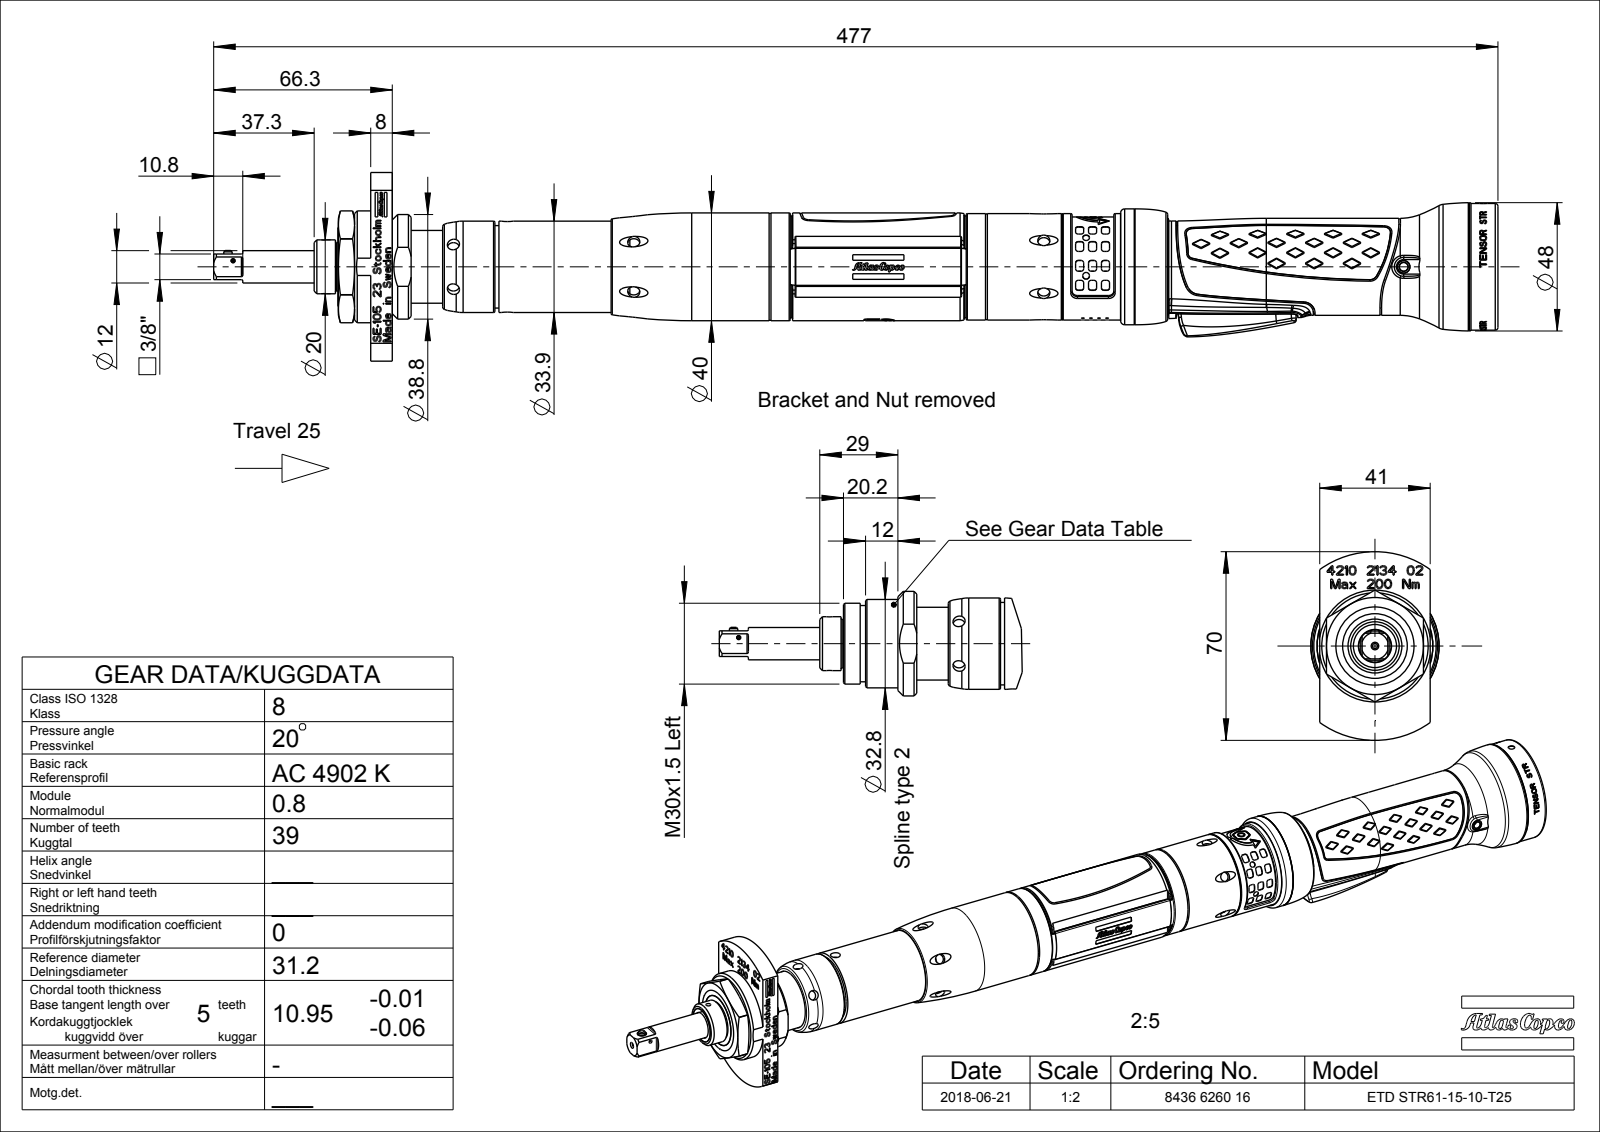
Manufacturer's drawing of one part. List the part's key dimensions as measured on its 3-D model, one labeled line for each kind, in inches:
Part name (STEP PRODUCT): E1_SW0006; E2_SW0004; ASM0098_ASM
STEP written by: CREO PARAMETRIC BY PTC INC, 2022414 (CONFIG_CONTROL_DESIGN)
Units: inches
Bodies: 3 solids, 4825 faces (1919 planar, 737 cylindrical, 2169 other)
Overall size (bounding box): 18.792 × 2.756 × 1.875
Volume: 29.77 in³ · Surface area: 139.4 in²
Round holes (diameter × count): ⌀0.02 ×30, ⌀0.039 ×12, ⌀0.177 ×10, ⌀0.063 ×2, ⌀0.015 ×1, ⌀0.059 ×1, ⌀0.075 ×1, ⌀0.087 ×1, ⌀0.118 ×1, ⌀0.126 ×1, ⌀0.154 ×1, ⌀0.185 ×1
Round bosses / shafts (diameter × count): ⌀1.85 ×1, ⌀1.693 ×1, ⌀1.634 ×1, ⌀1.575 ×1, ⌀1.555 ×1, ⌀1.476 ×1, ⌀1.457 ×1, ⌀1.425 ×1
Partial cylindrical surfaces — rounded edges, fillets, slot ends (radius × count): R0.008 ×58, R0.012 ×44, R0.02 ×43, R0.079 ×14, R0.118 ×12, R0.059 ×5, R0.016 ×4, R0.024 ×4
Main face-to-face distances: 0.02, 16.181, 0.315, 16.496, 7.793, 8.389, 8.704, 0.143, 7.65, 8.531
Hole centre spacings: 0.189, 0.118, 0.378, 0.236, 0.354, 2.656, 5.973, 8.629
